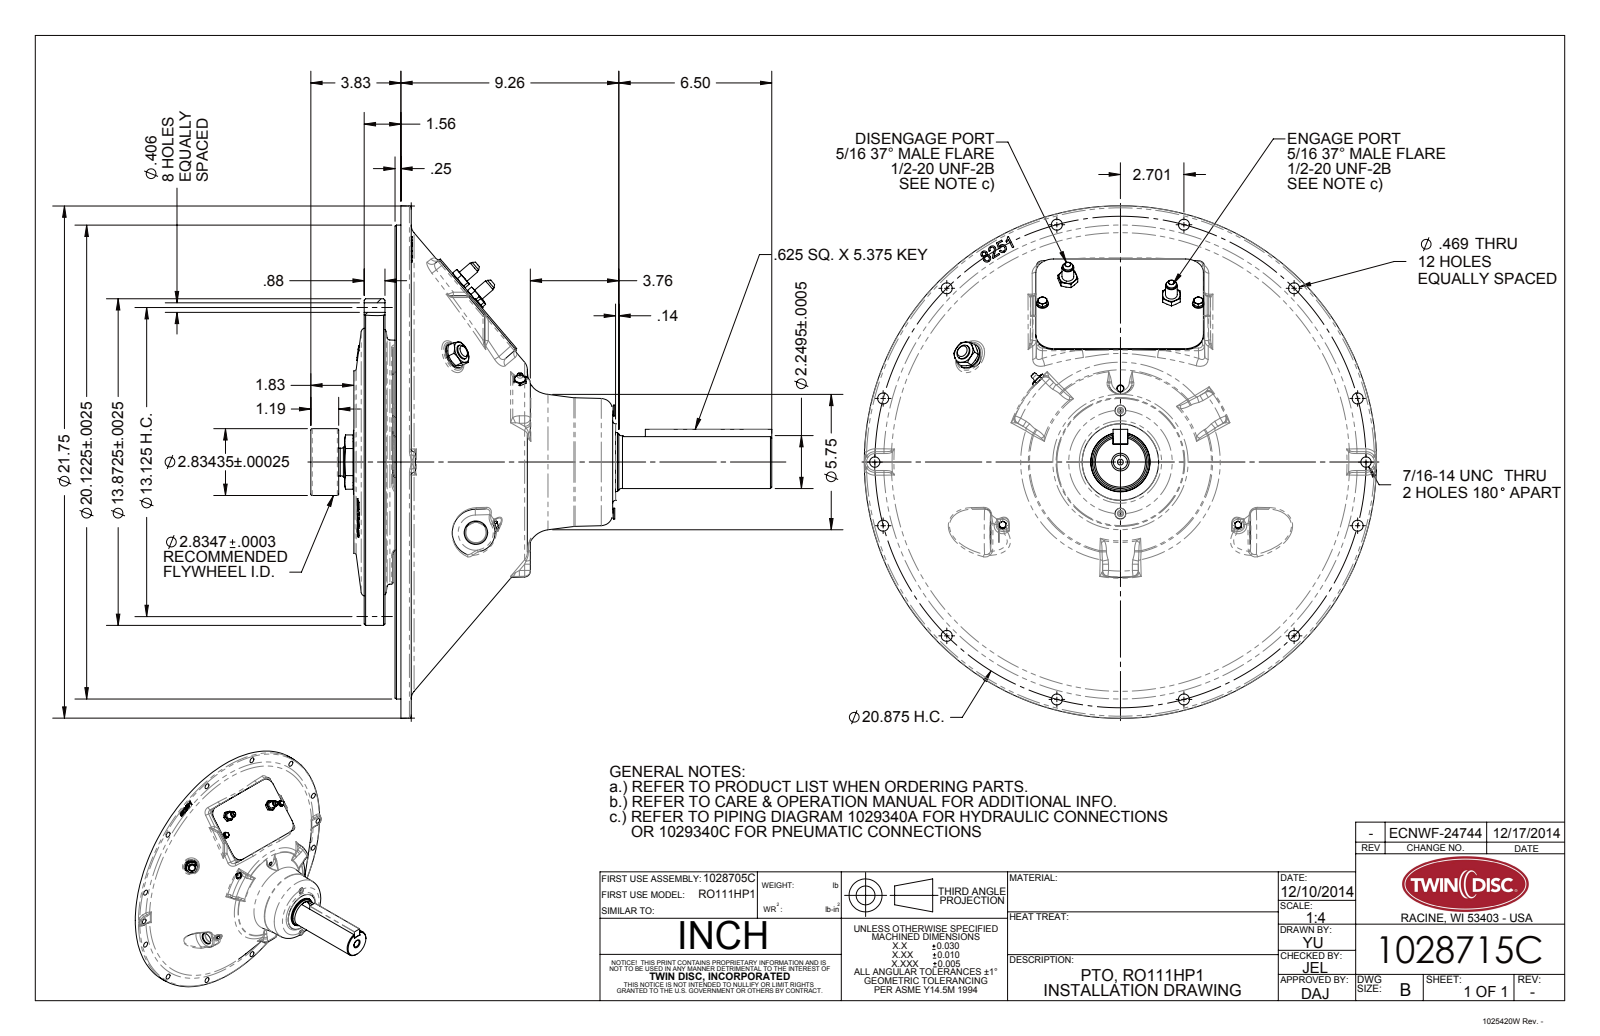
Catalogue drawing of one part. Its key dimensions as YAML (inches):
part_name: "1028715C"
step_written_by: "SolidWorks 2010 (AUTOMOTIVE_DESIGN)"
units: inches
bodies: {solids: 0, faces: 922, planar: 245, cylindrical: 190, other: 487}
overall_size: [21.773, 21.773, 19.594]
round_holes:
  - {diameter: 0.469, count: 12}
  - {diameter: 0.406, count: 8}
  - {diameter: 0.234, count: 2}
  - {diameter: 0.375, count: 2}
  - {diameter: 0.422, count: 2}
  - {diameter: 0.437, count: 2}
  - {diameter: 0.875, count: 2}
  - {diameter: 0.313, count: 1}
  - {diameter: 0.998, count: 1}
  - {diameter: 1.181, count: 1}
  - {diameter: 1.936, count: 1}
  - {diameter: 2.428, count: 1}
round_bosses_or_shafts:
  - {diameter: 0.5, count: 4}
  - {diameter: 0.46, count: 2}
  - {diameter: 0.426, count: 2}
  - {diameter: 20.122, count: 1}
  - {diameter: 20.12, count: 1}
  - {diameter: 13.872, count: 1}
  - {diameter: 11.375, count: 1}
  - {diameter: 2.834, count: 1}
partial_cylinders:
  - {radius: 0.25, count: 18}
  - {radius: 0.08, count: 14}
  - {radius: 0.15, count: 6}
  - {radius: 0.125, count: 4}
  - {radius: 0.75, count: 4}
  - {radius: 2.052, count: 4}
  - {radius: 0.01, count: 2}
  - {radius: 0.1, count: 2}
face_to_face_distances: [1.387, 0.437, 1.824, 1.997, 1.56, 0.173, 0.064, 2.436, 1.998, 0.612]
hole_center_spacings: [10.437, 7.426, 12.329, 20.164, 4.437, 5.023, 5.403, 5.776]
